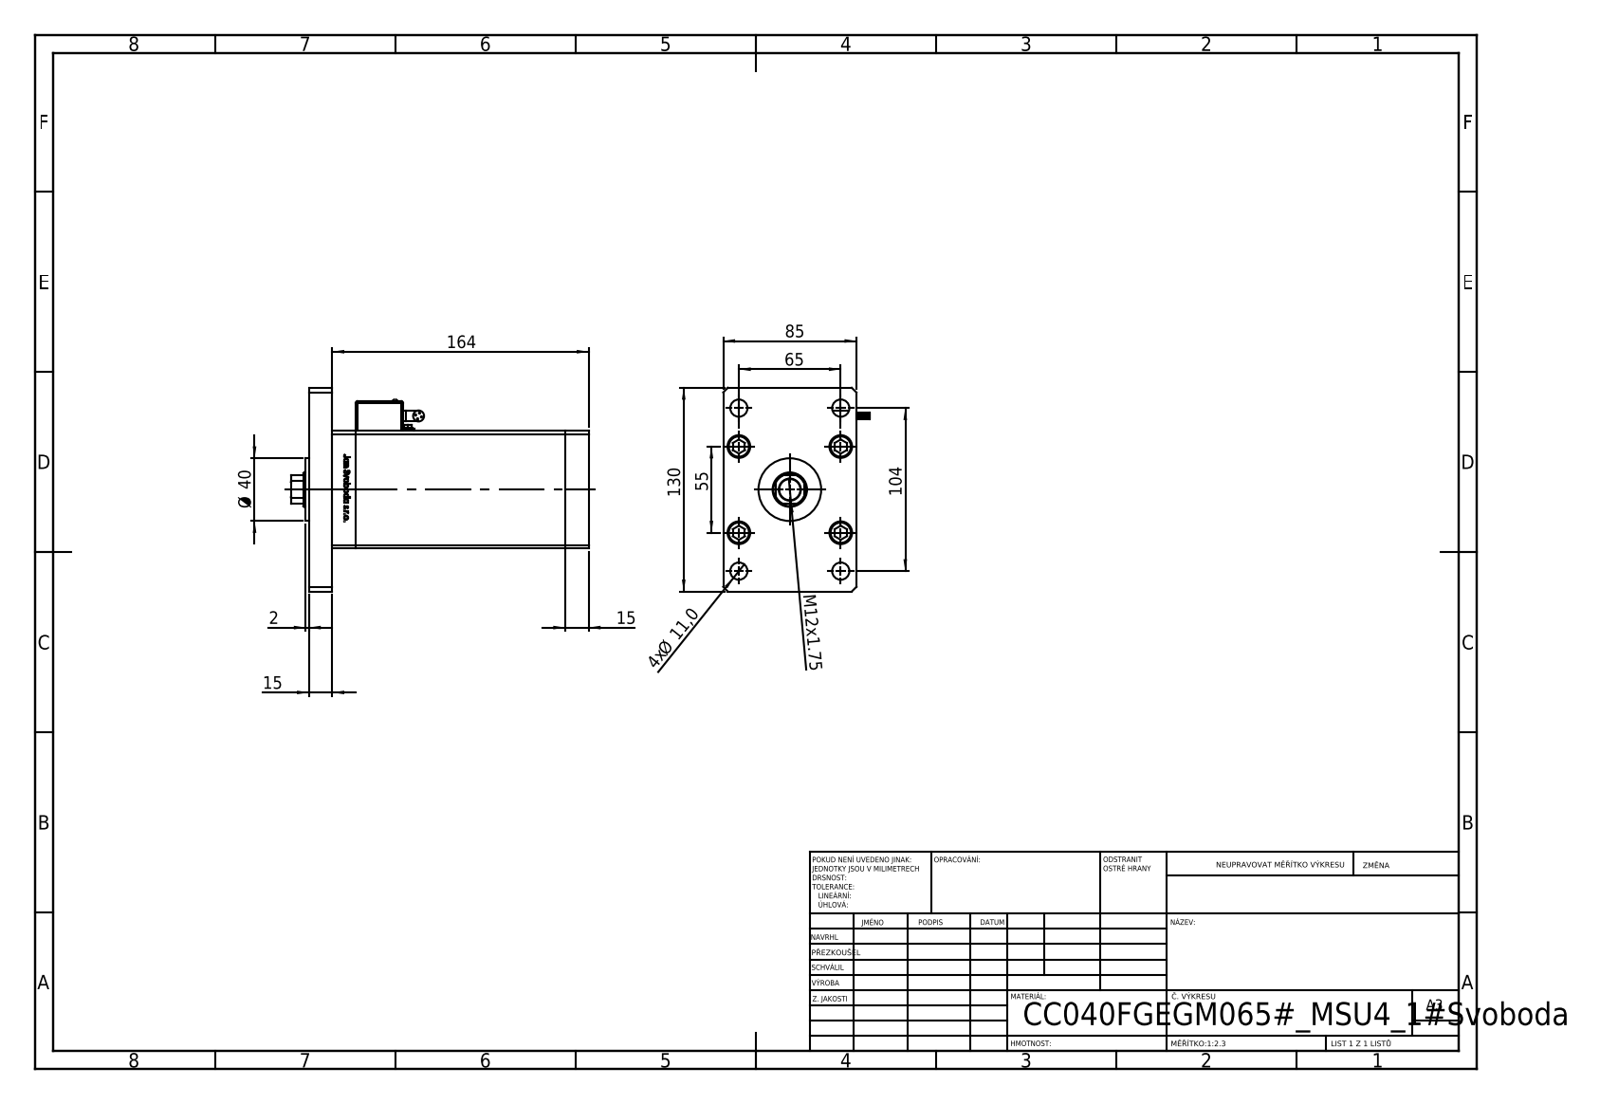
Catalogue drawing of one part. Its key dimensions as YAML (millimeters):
part_name: "V220C_FRONT_F; Magnetic_Switch_MSU4; V220C_F; V220C_VC_F (+3 more)"
step_written_by: "SolidWorks 2019 (CONFIG_CONTROL_DESIGN)"
units: millimeters
bodies: {solids: 20, faces: 1412, planar: 556, cylindrical: 232, other: 624}
overall_size: [190, 130, 93.3]
volume: 1105000
surface_area: 196536
round_holes:
  - {diameter: 11, count: 9}
  - {diameter: 15.5, count: 5}
  - {diameter: 10, count: 4}
  - {diameter: 14.5, count: 4}
  - {diameter: 2, count: 2}
  - {diameter: 13.16, count: 2}
  - {diameter: 3.6, count: 1}
  - {diameter: 5, count: 1}
  - {diameter: 7, count: 1}
  - {diameter: 13.5, count: 1}
  - {diameter: 22, count: 1}
  - {diameter: 23.5, count: 1}
round_bosses_or_shafts:
  - {diameter: 8, count: 9}
  - {diameter: 14.5, count: 5}
  - {diameter: 0.85, count: 4}
  - {diameter: 7, count: 2}
  - {diameter: 40, count: 1}
  - {diameter: 6, count: 1}
  - {diameter: 3.5, count: 1}
  - {diameter: 2.5, count: 1}
partial_cylinders:
  - {radius: 1, count: 14}
  - {radius: 0.93, count: 2}
  - {radius: 4, count: 2}
  - {radius: 10.5, count: 1}
face_to_face_distances: [15, 148.5, 163.5, 85, 30, 75, 133.5, 178.5, 10.5, 27.5]
hole_center_spacings: [28, 24.5, 42.57, 61.32, 65, 69.46, 79.5, 102.69]
